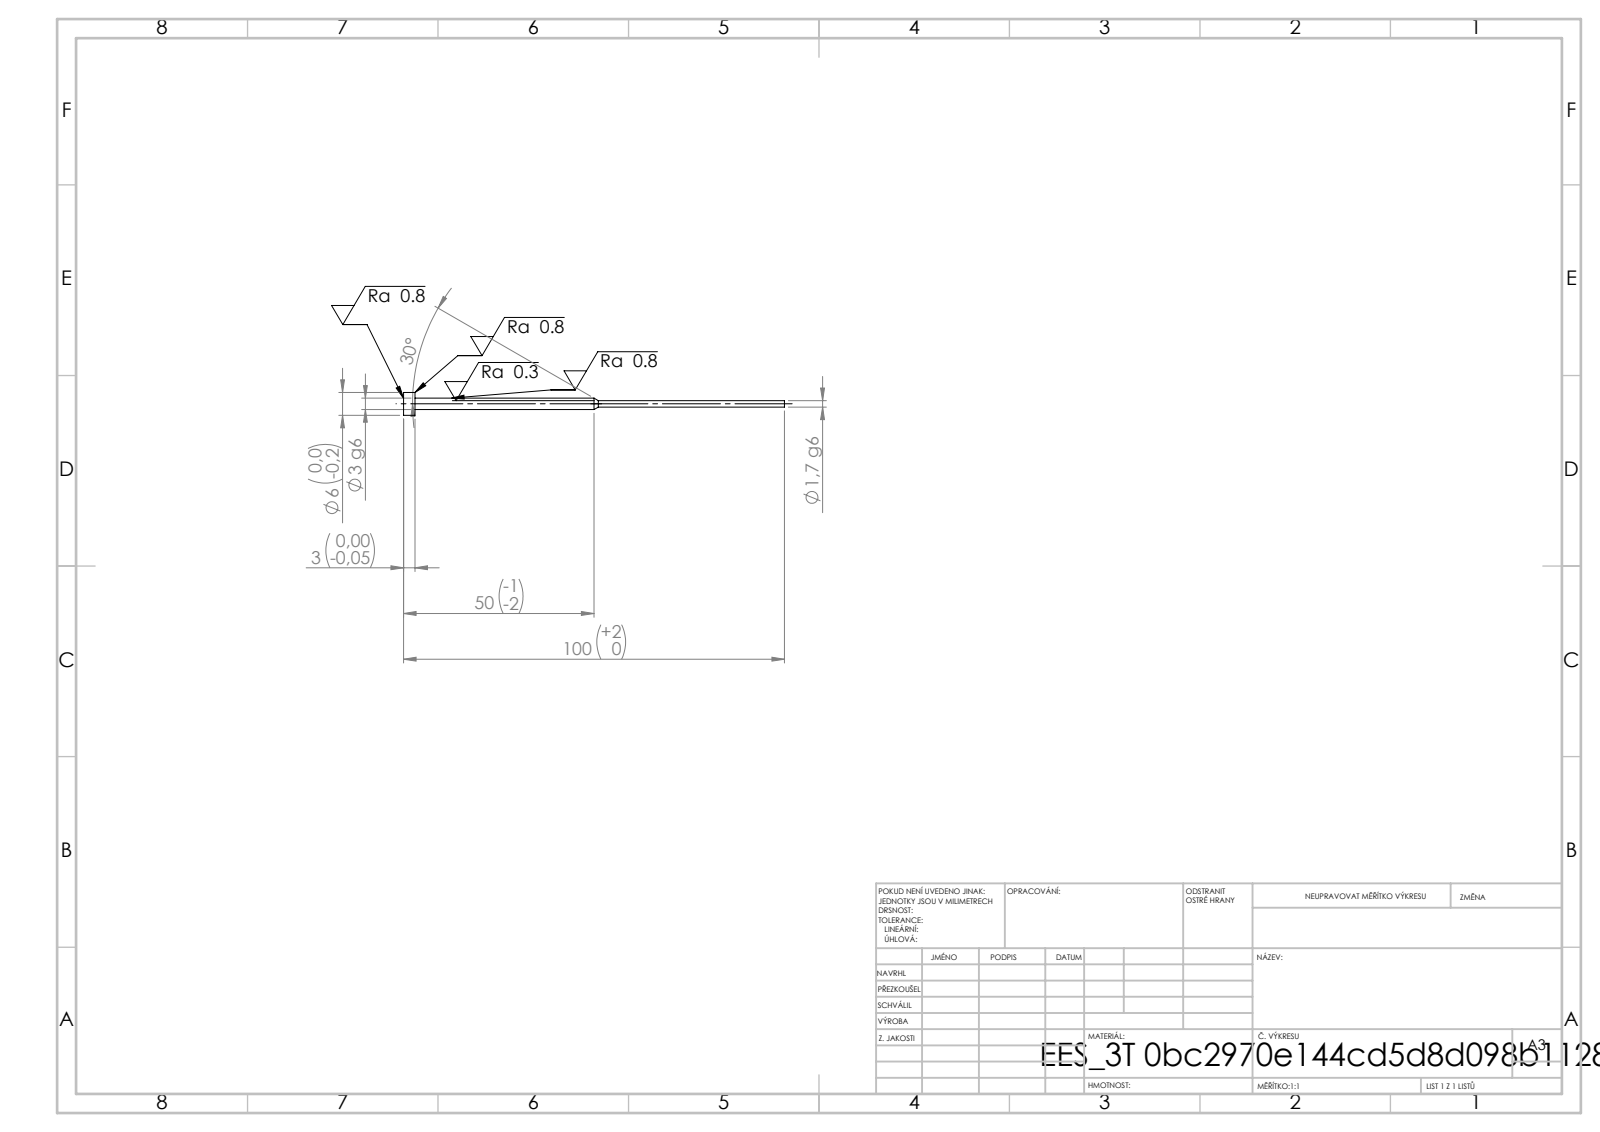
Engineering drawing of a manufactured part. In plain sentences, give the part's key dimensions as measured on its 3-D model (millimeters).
Its 3-D file was written by "SolidWorks 2019 (CONFIG_CONTROL_DESIGN)". It is 1 solid with 11 faces: 3 planar, 6 cylindrical and 2 other. Overall it measures 100 by 6 by 6 millimeters. Its volume is 533 cubic millimeters and its surface area 822 square millimeters. Round bosses or shafts: 1 of diameter 6, 1 of diameter 3, 1 of diameter 1.7. The main face-to-face distances are 3, 97, 100.
